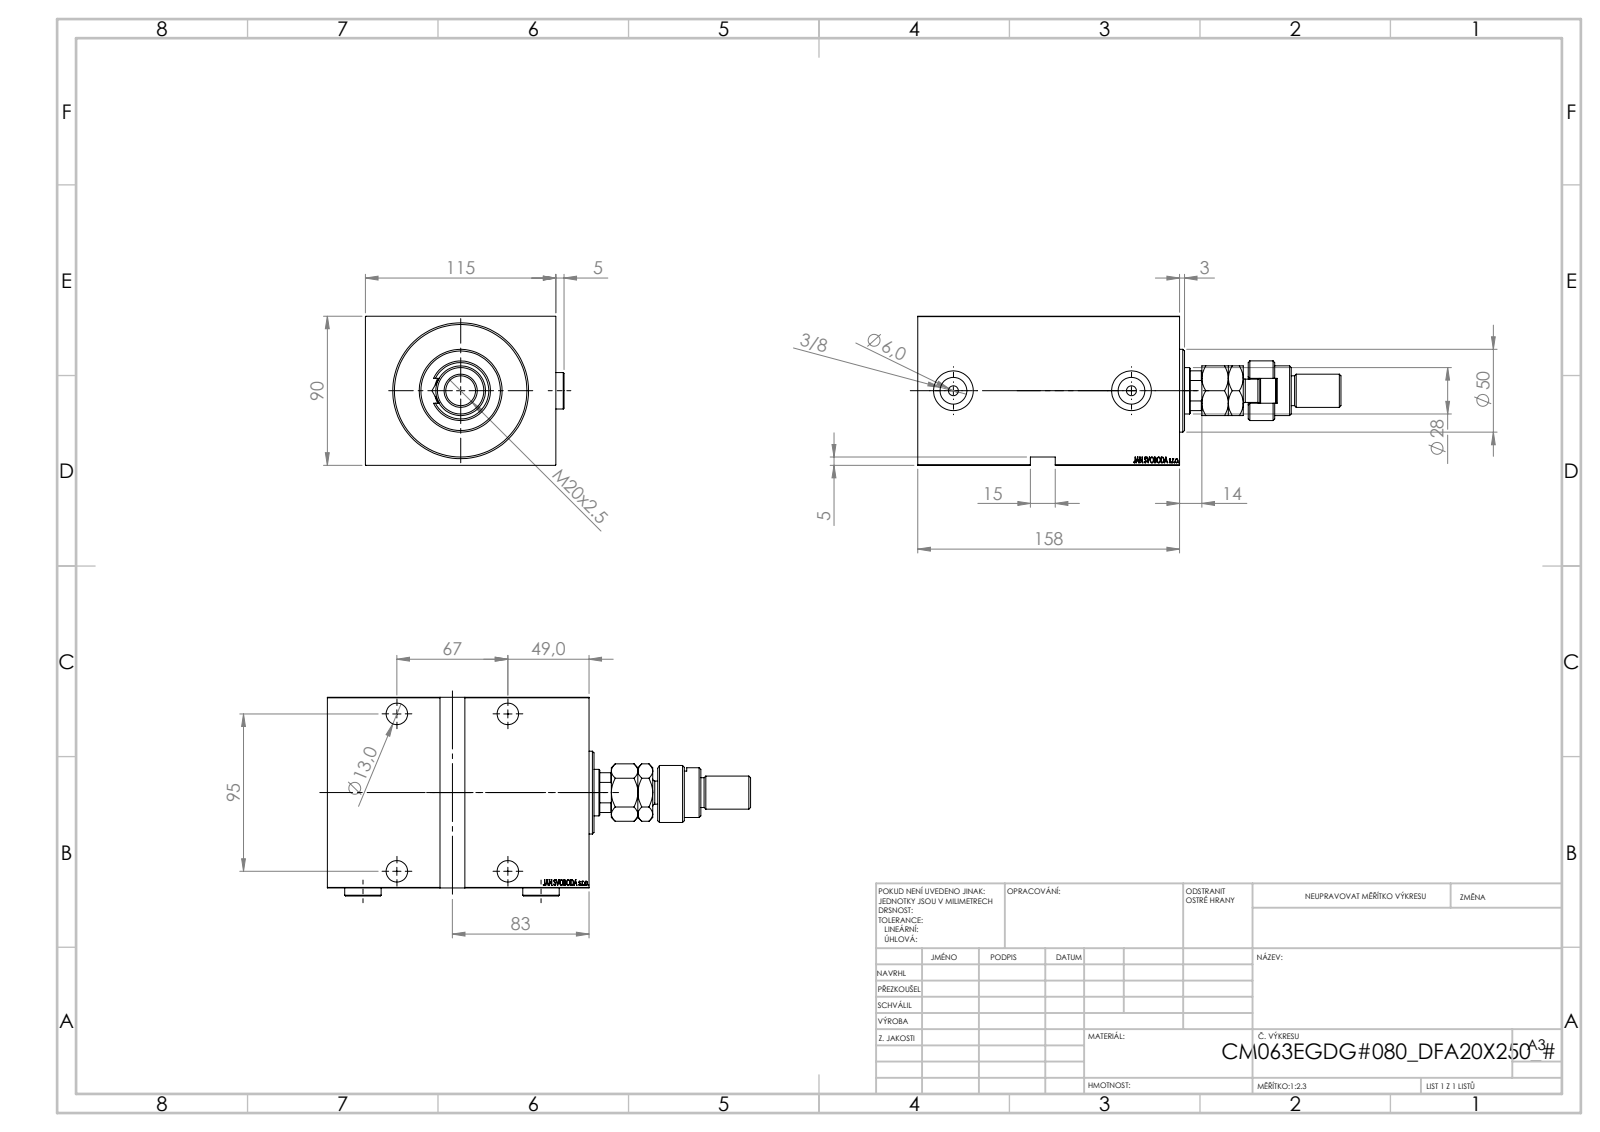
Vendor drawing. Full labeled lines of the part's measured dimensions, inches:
Part name (STEP PRODUCT): V450CM_E_Body; V450CM_VC_B; FEMALE_PART_FOR_DFA; Zatka_OIL_PORT (+2 more)
STEP written by: SolidWorks 2019 (CONFIG_CONTROL_DESIGN)
Units: inches
Bodies: 7 solids, 997 faces (474 planar, 81 cylindrical, 442 other)
Overall size (bounding box): 10.059 × 4.72 × 3.543
Volume: 86.59 in³ · Surface area: 294.1 in²
Round holes (diameter × count): ⌀0.512 ×4, ⌀0.748 ×4, ⌀0.236 ×2, ⌀0.637 ×2, ⌀0.945 ×2, ⌀0.728 ×1, ⌀1.102 ×1, ⌀1.24 ×1, ⌀2.48 ×1, ⌀3.15 ×1
Round bosses / shafts (diameter × count): ⌀0.866 ×3, ⌀2.559 ×1, ⌀1.969 ×1, ⌀1.417 ×1, ⌀1.181 ×1, ⌀0.787 ×1, ⌀0.709 ×1, ⌀0.551 ×1
Partial cylindrical surfaces — rounded edges, fillets, slot ends (radius × count): R0.295 ×1, R0.472 ×1, R0.531 ×1
Main face-to-face distances: 3.543, 4.528, 6.22, 0.689, 5.531, 0.197, 6.024, 5.335, 3.484, 2.539
Hole centre spacings: 2.638, 3.74, 4.577, 4.232
